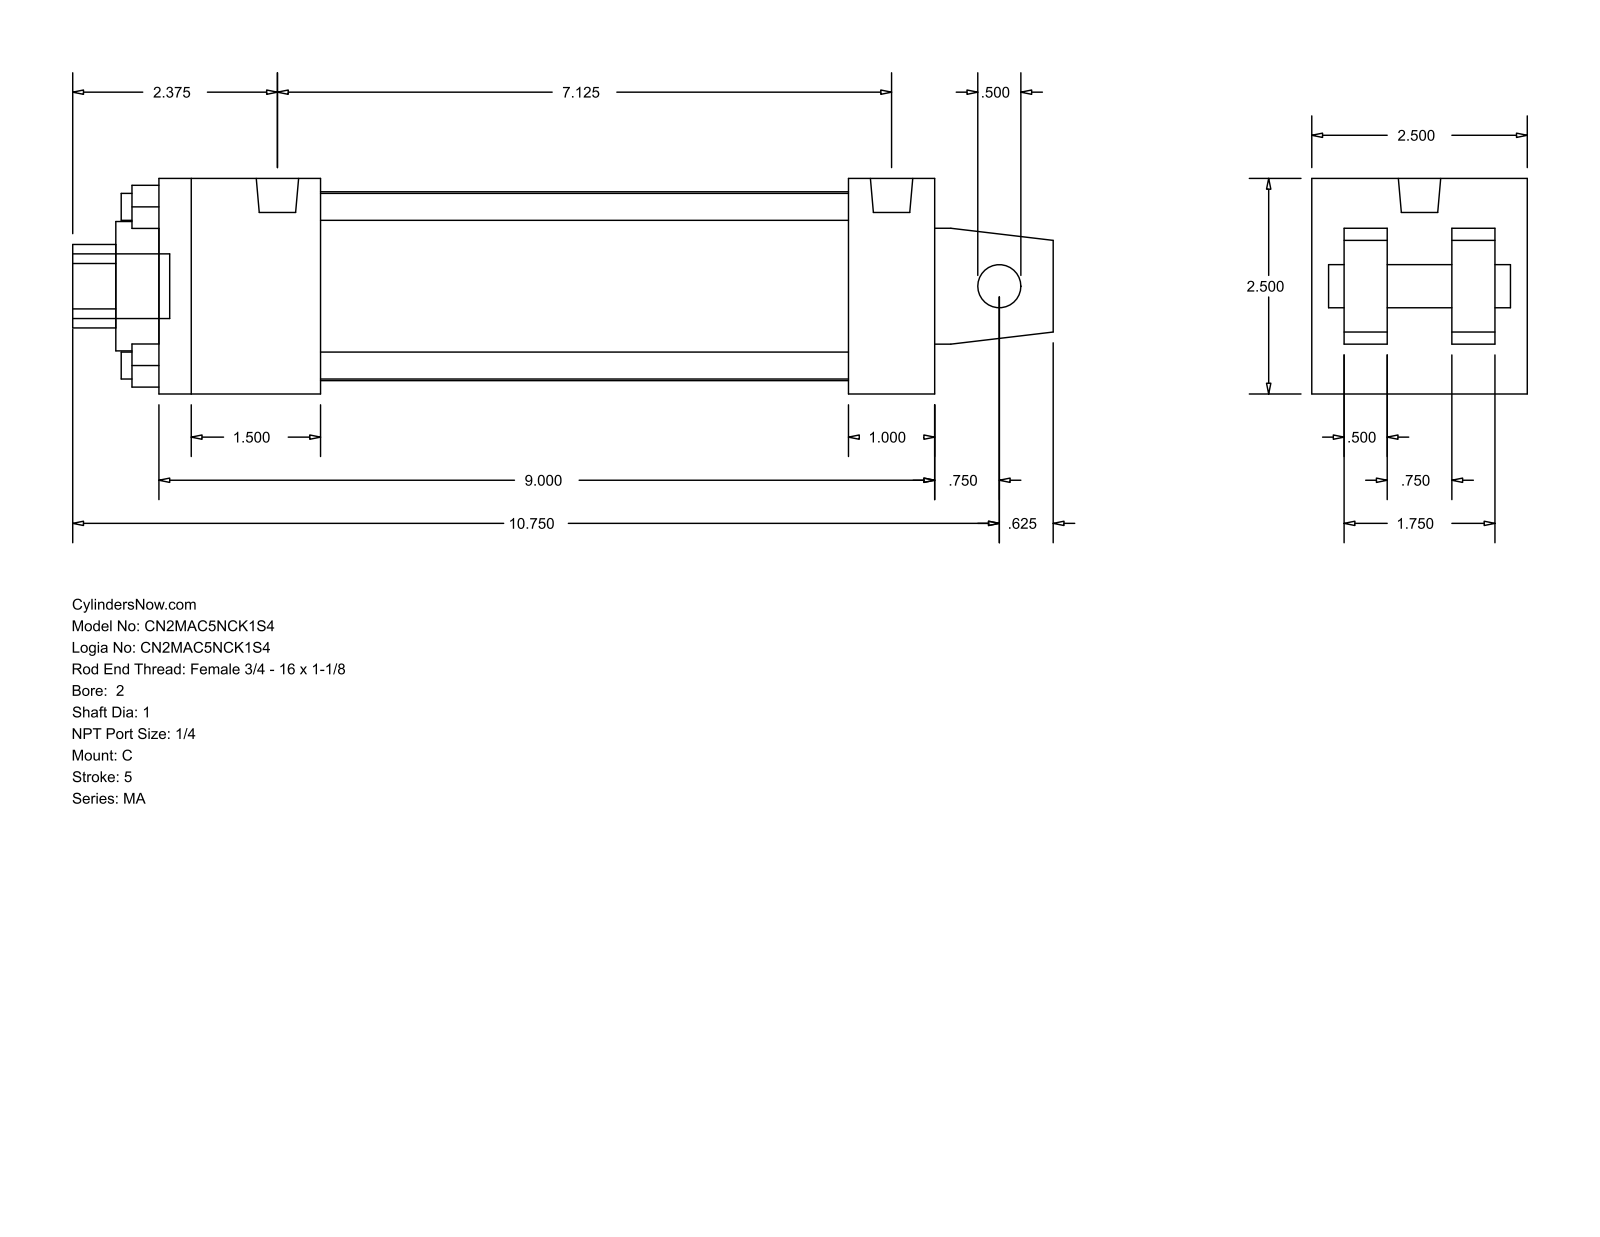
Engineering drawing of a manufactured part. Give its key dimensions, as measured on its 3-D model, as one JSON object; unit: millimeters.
{"part_name": "MA_C__0200_1", "step_written_by": "GSSL Pune (CONFIG_CONTROL_DESIGN)", "units": "millimeters", "bodies": {"solids": 0, "faces": 103, "planar": 76, "cylindrical": 27, "other": 0}, "overall_size": [288.93, 63.5, 63.5], "round_holes": [[7.94, 4], [12.7, 1], [25.4, 1], [38.1, 1], [55.63, 1]], "round_bosses_or_shafts": [[7.94, 4], [12.49, 2], [19.05, 1]], "partial_cylinders_radius": [[12.29, 1]], "face_to_face_distances": [63.5, 12.7, 228.6, 22.22, 41.28, 9.52, 53.98, 31.76, 47.63, 25.4], "hole_center_spacings": [33.05, 46.74, 66.1]}
